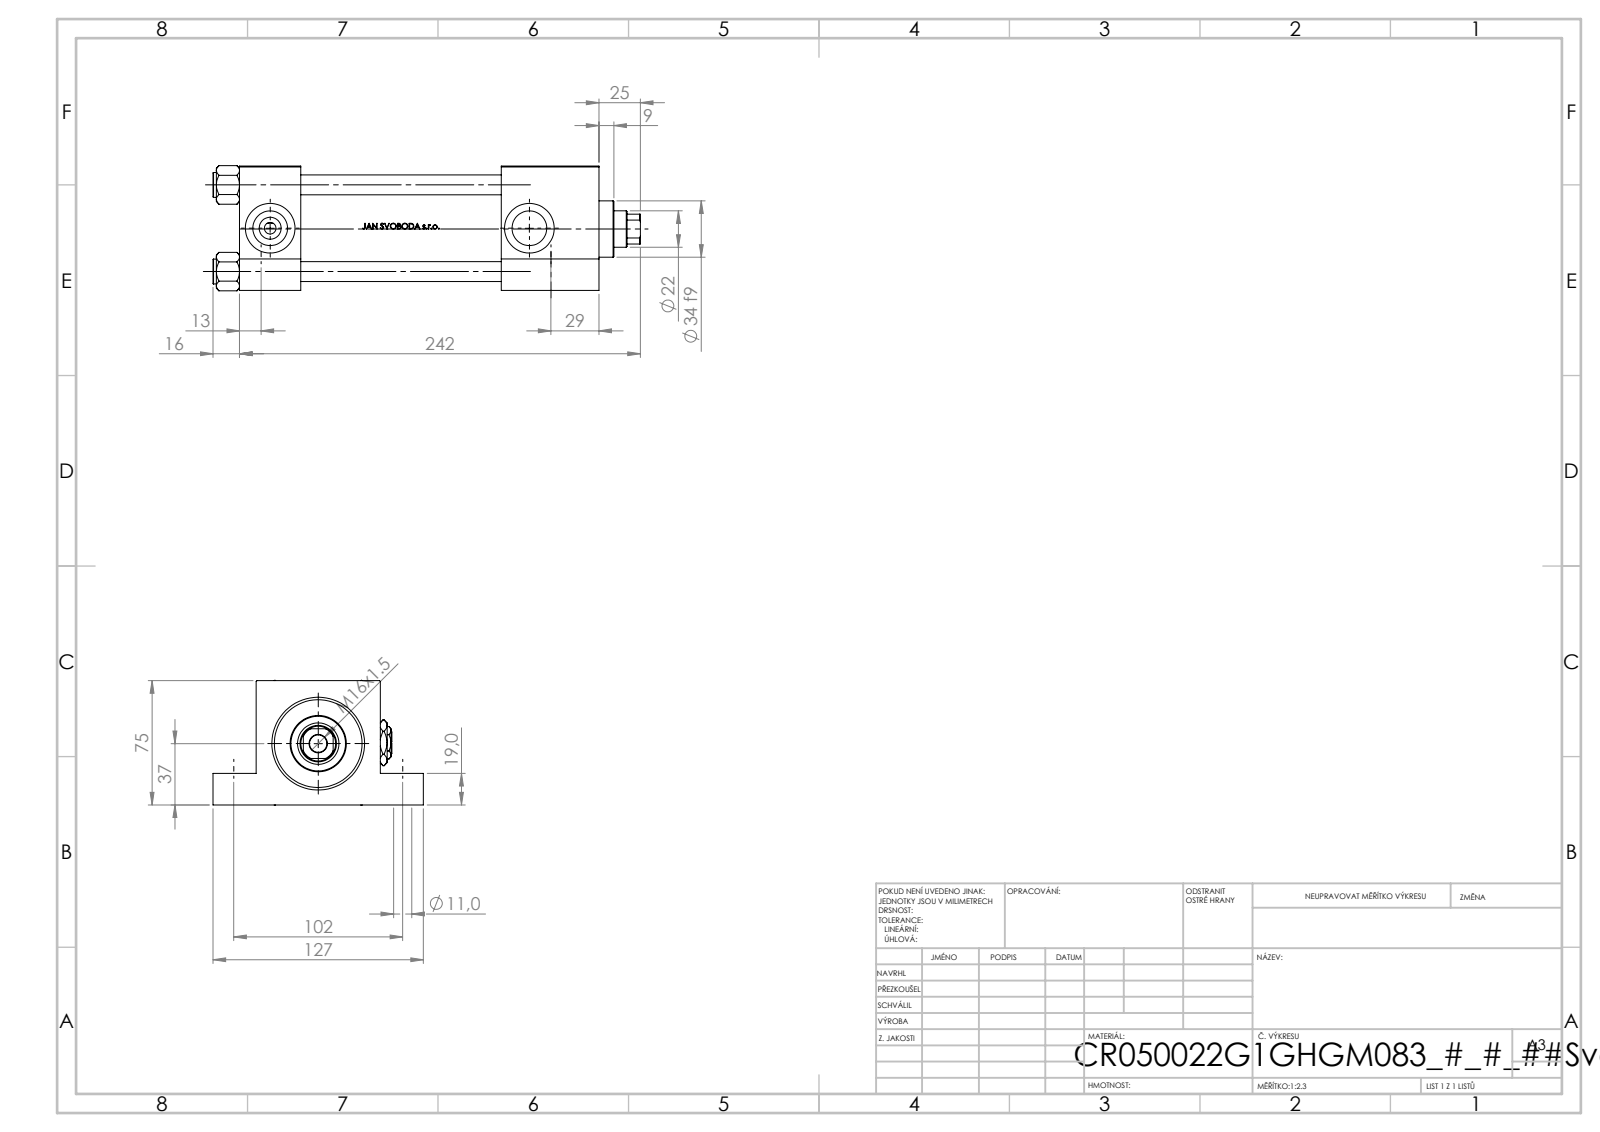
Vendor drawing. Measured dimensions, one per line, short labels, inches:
name: Zatka_pro_OIL_PORT; V215CR_VCP_G; V215CR_G_Body; V215CR_G_TYCINKA (+2 more)
written by: SolidWorks 2019 (CONFIG_CONTROL_DESIGN)
unit: in
bodies: 12 solids, 1134 faces (454 planar, 128 cylindrical, 552 other)
size: 10.157 × 5 × 2.974
volume: 51.04 in³; area: 304 in²
holes: 4× ⌀0.433, 4× ⌀0.472, 2× ⌀0.276, 2× ⌀0.825, 2× ⌀1.181, 1× ⌀0.413, 1× ⌀0.866, 1× ⌀0.984, 1× ⌀1.614, 1× ⌀1.969, 1× ⌀2.087
bosses: 4× ⌀0.591, 1× ⌀2.205, 1× ⌀1.339
rounds: 1× R0.413
face distances: 2.953, 1.457, 8.543, 7.087, 0.748, 2.205, 6.22, 4.764, 2.323, 1.024
hole spacings: 2.059, 1.442, 1.47, 2.912, 4.016, 6.89, 7.975, 6.161
